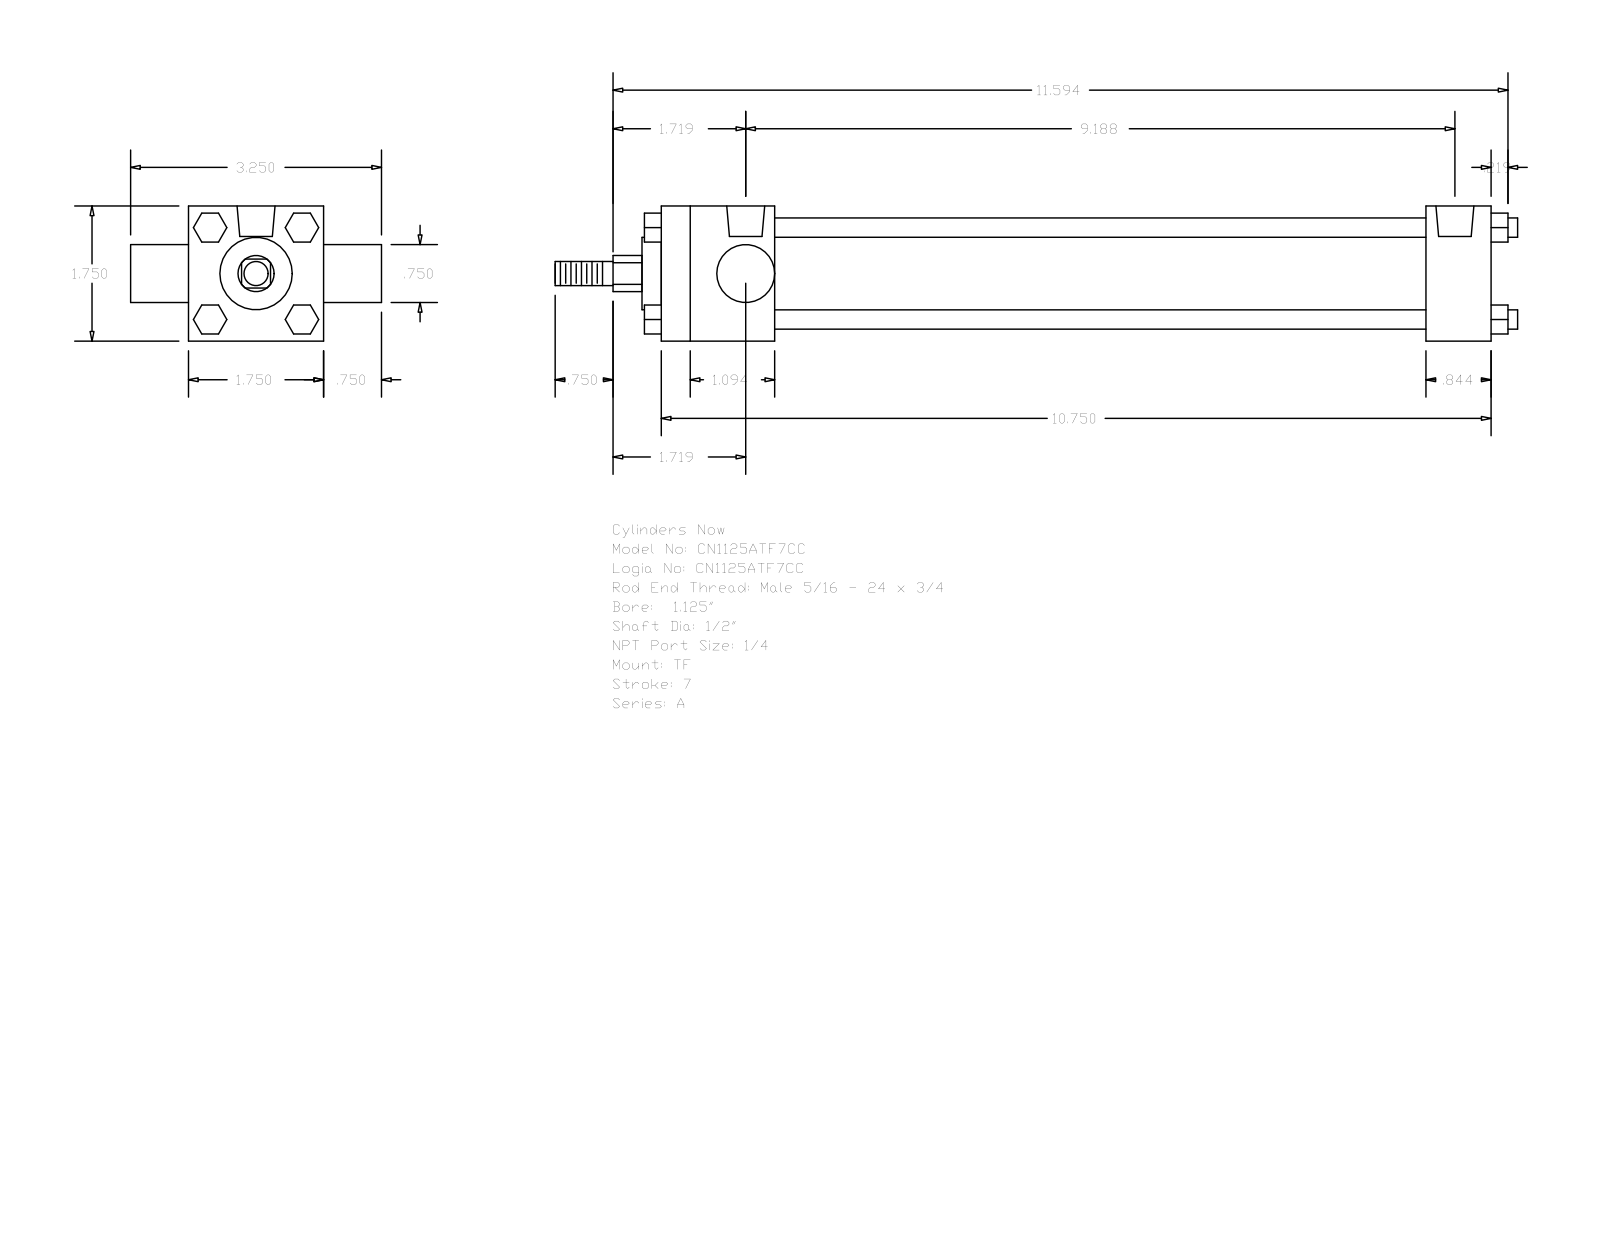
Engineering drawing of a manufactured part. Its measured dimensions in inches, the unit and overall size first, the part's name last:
Units: inches
Overall size (bounding box): 12.469 × 3.25 × 1.75
Round holes (diameter × count): ⌀0.219 ×3, ⌀0.492 ×2
Round bosses / shafts (diameter × count): ⌀0.25 ×4, ⌀1.255 ×1, ⌀0.937 ×1, ⌀0.75 ×1, ⌀0.5 ×1, ⌀0.313 ×1
Partial cylindrical surfaces — rounded edges, fillets, slot ends (radius × count): R0.234 ×1
Main face-to-face distances: 1.75, 10.75, 9.906, 0.844, 1.469, 8.437, 9.281, 0.75, 2.5, 0.375
Hole centre spacings: 0.062, 0.063, 9.063, 9.125, 9.125, 9.187
Bodies: 0 solids, 120 faces (92 planar, 28 cylindrical, 0 other)
Part name (STEP PRODUCT): A_TF__0112_0.5
STEP written by: GSSL Pune (CONFIG_CONTROL_DESIGN)
